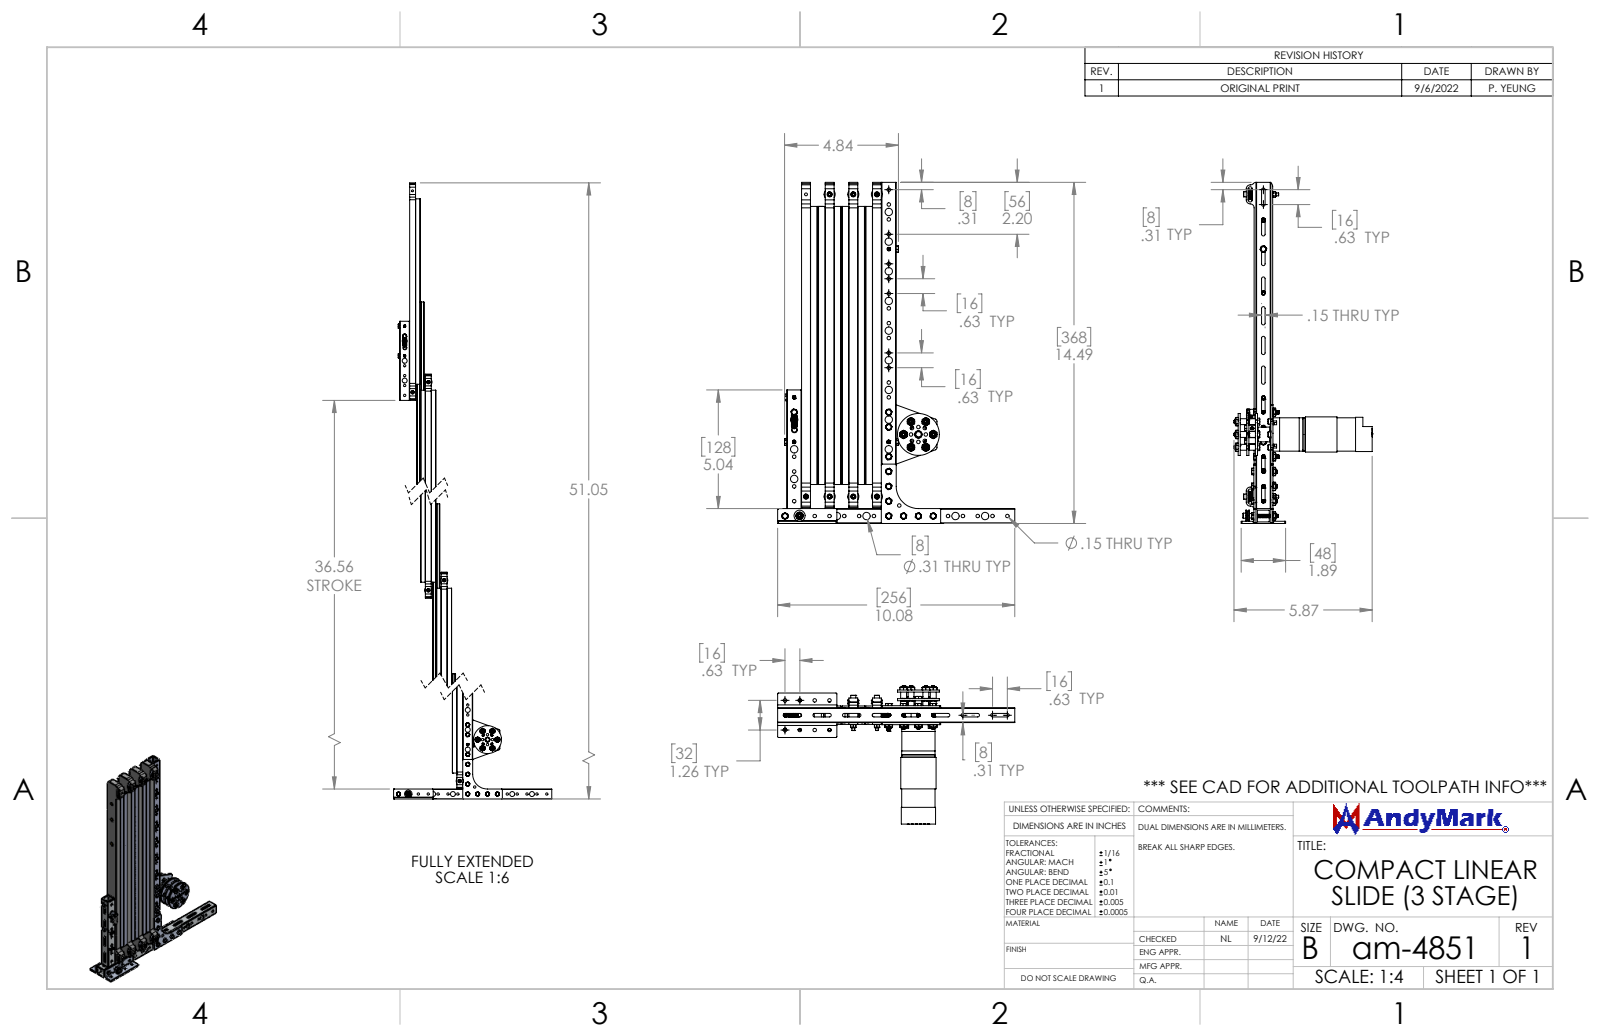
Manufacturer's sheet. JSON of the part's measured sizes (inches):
{"part_name": "625x500 Aluminum Spacer am-3720_92510A777; am-4376 17T 0.5mod NeveRest Orbital Pinion; Pulley Holder Assy_Add a Stage Pulley Holder; am-4610b NeveRest Orbital 14 Gearmotor (+8 more)", "step_written_by": "SolidWorks 2022 (AUTOMOTIVE_DESIGN)", "units": "inches", "bodies": {"solids": 316, "faces": 15379, "planar": 1670, "cylindrical": 6446, "other": 7263}, "overall_size": [14.488, 10.079, 5.881], "volume_in3": 41.85, "surface_area_in2": 702.1, "round_holes": [[0.15, 69], [0.116, 54], [0.315, 28], [0.111, 18], [0.191, 18], [0.125, 12], [0.15, 12], [0.098, 10], [0.118, 9], [0.141, 7], [0.171, 7], [0.262, 7]], "round_bosses_or_shafts": [[0.138, 25], [0.217, 16], [0.118, 9], [0.472, 8], [0.378, 7], [0.25, 7], [0.093, 6], [0.218, 4]], "partial_cylinders_radius": [[0.008, 120], [0.075, 38], [0.064, 34], [0.075, 24], [0.058, 18], [0.039, 13], [0.01, 12], [0.025, 12]], "face_to_face_distances": [0.63, 2.01, 1.005, 1.005, 1.38, 0.063, 0.567, 0.079, 0.709, 0.375], "hole_center_spacings": [1.26, 0.63, 2.52, 1.89, 3.78, 0.315, 0.945, 2.205]}
